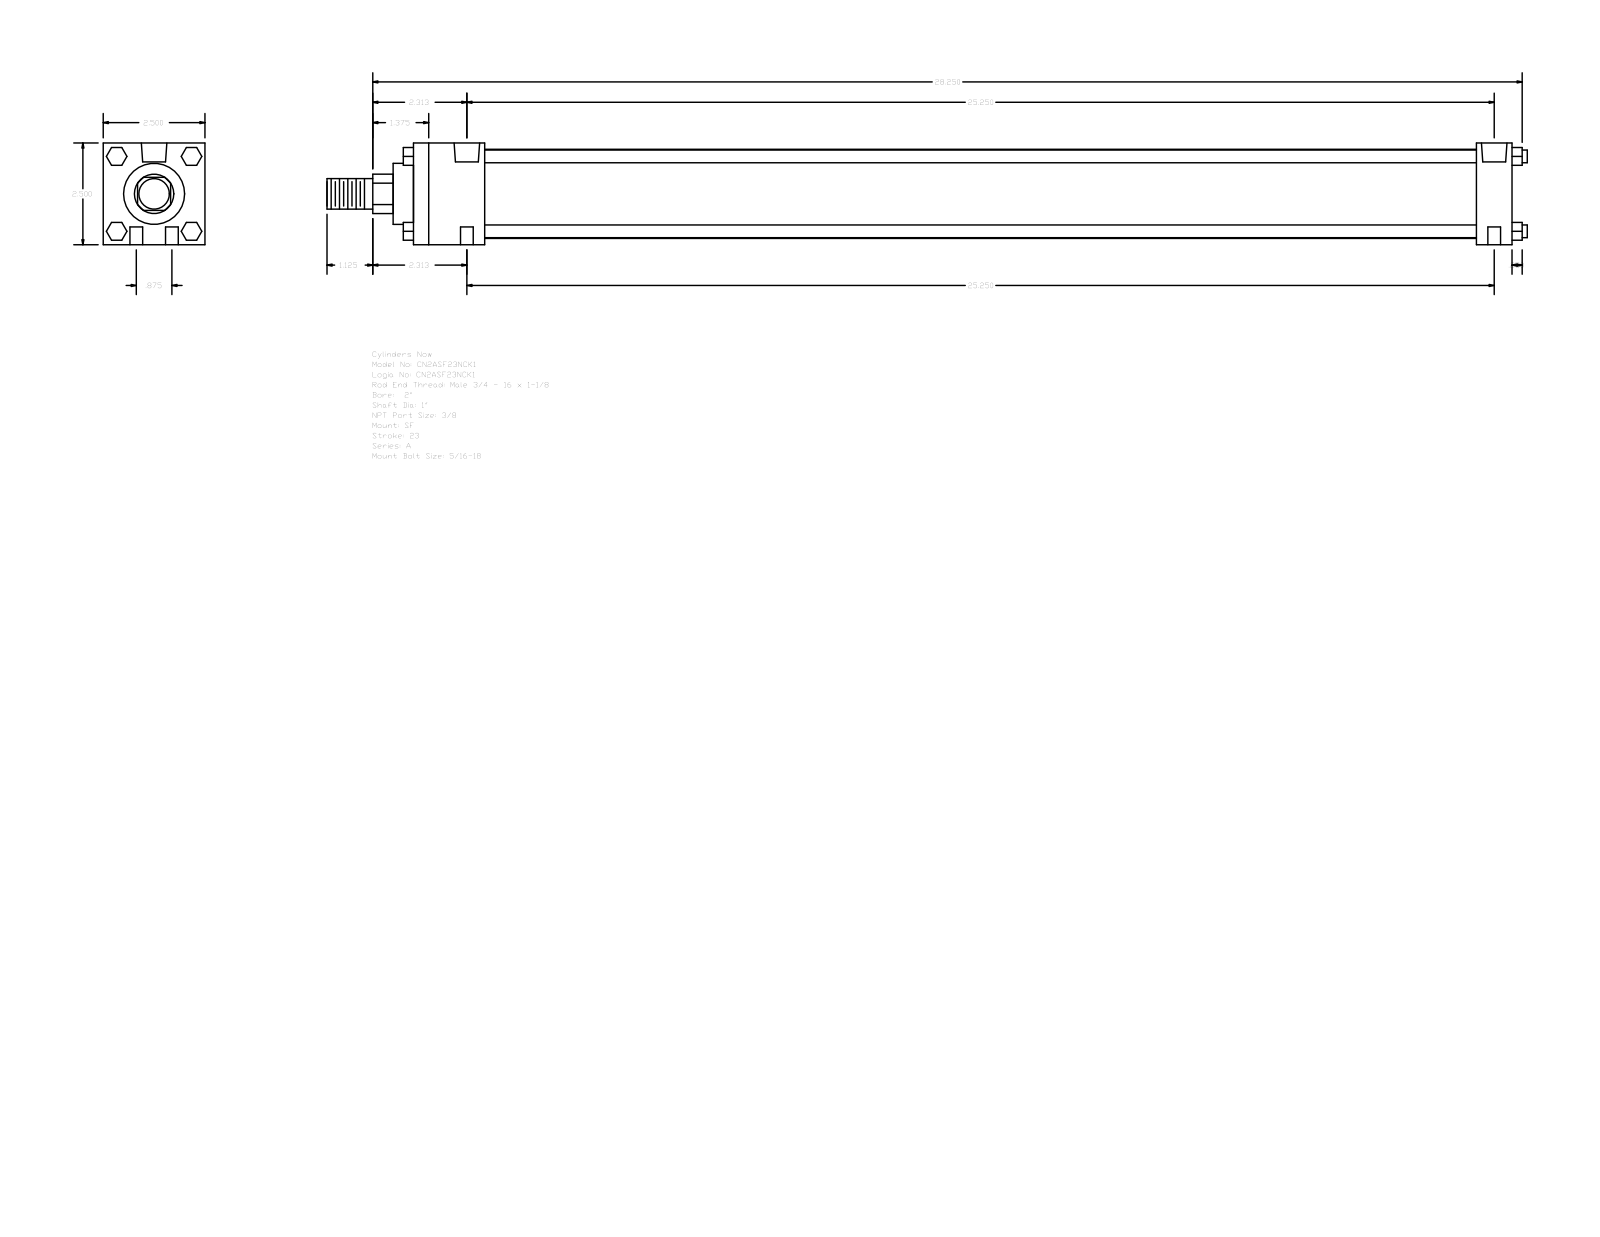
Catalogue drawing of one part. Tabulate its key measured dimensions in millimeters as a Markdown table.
| quantity | value |
| --- | --- |
| part name | A_SF__0200_1 |
| STEP written by | GSSL Pune (CONFIG_CONTROL_DESIGN) |
| units | millimeters |
| bodies | 0 solids, 124 faces (94 planar, 30 cylindrical, 0 other) |
| overall size | 749.3 × 63.5 × 63.5 |
| round holes (diameter × count) | 7.94 × 4, 5.56 × 2, 15.93 × 2 |
| round bosses / shafts (diameter × count) | 7.94 × 4, 55.63 × 1, 38.1 × 1, 25.4 × 1, 19.05 × 1 |
| partial cylindrical surfaces (radius × count) | 12.29 × 1 |
| main face-to-face distances | 63.5, 685.8, 663.58, 22.22, 44.45, 619.13, 641.35, 12.7, 698.5, 6.35 |
| hole center spacings | 11.11, 641.45, 641.35, 22.22, 641.73, 635.78 |
